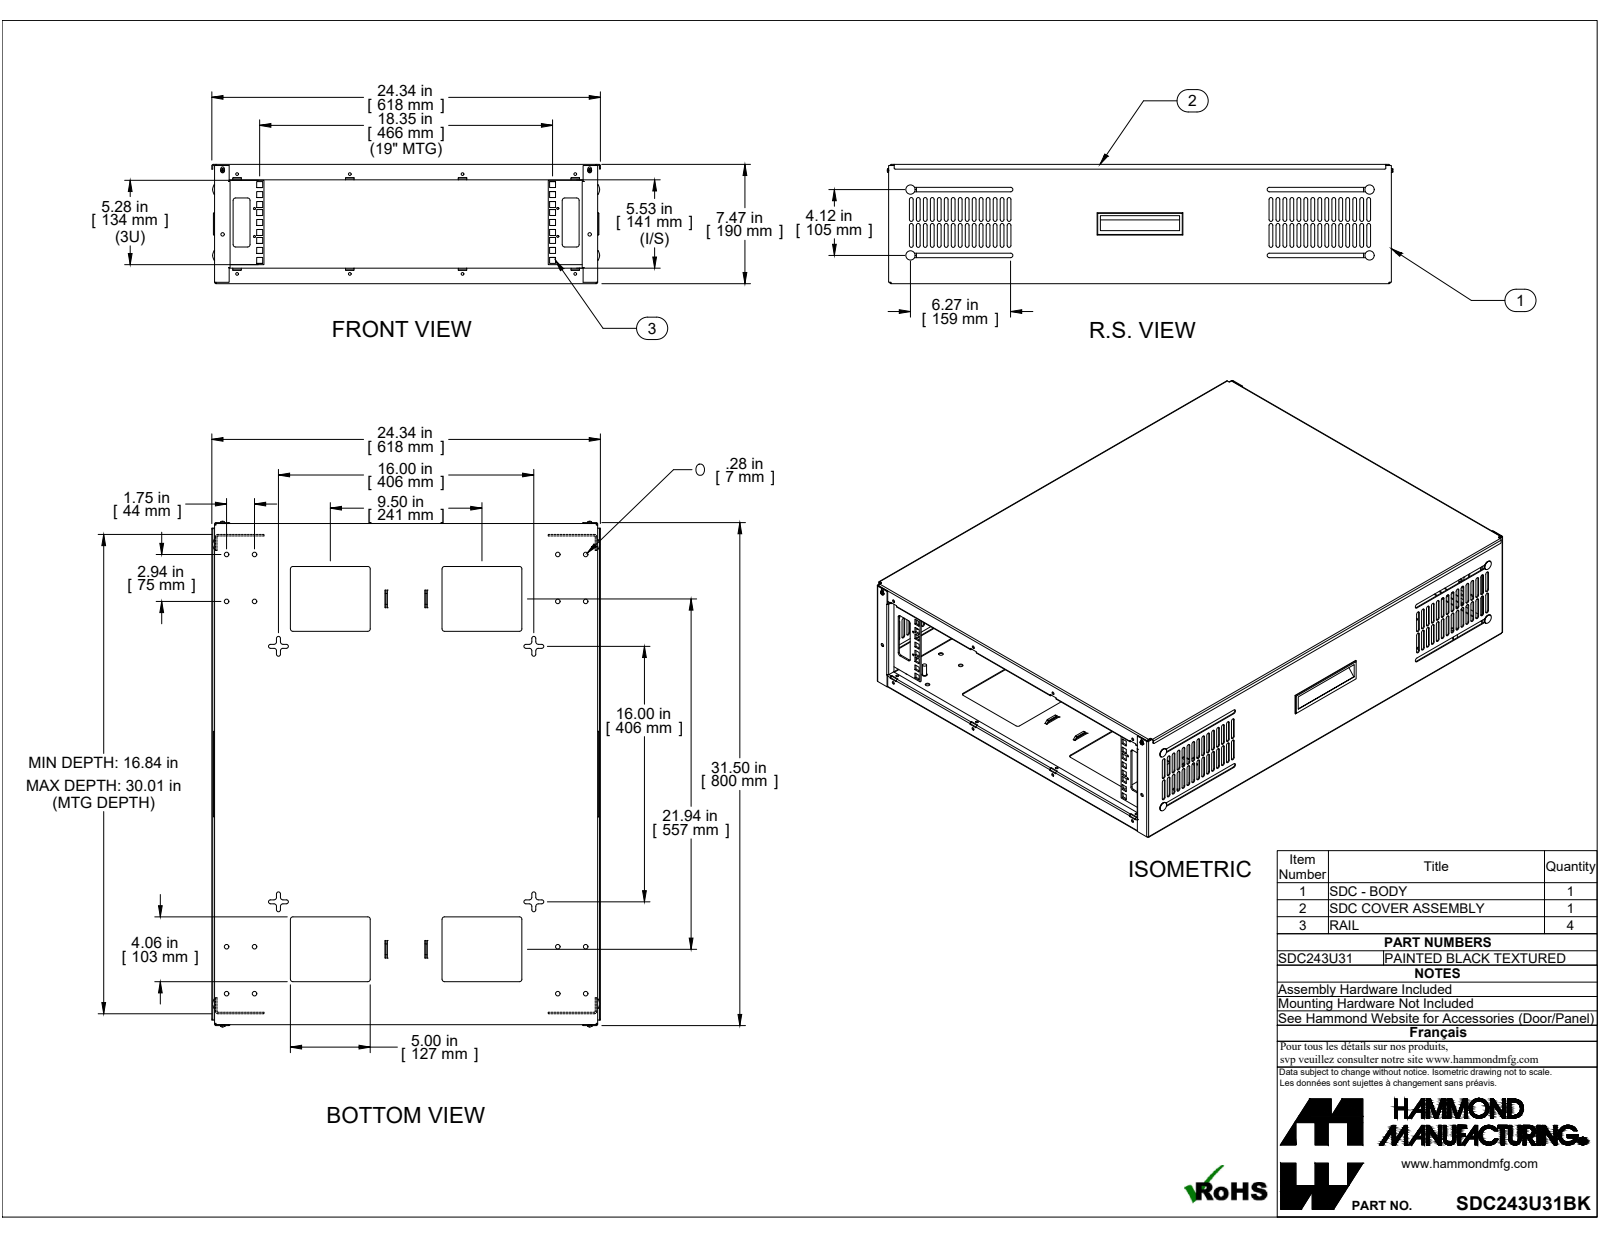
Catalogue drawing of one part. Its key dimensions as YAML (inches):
part_name: "SDC243U31BK"
step_written_by: "SolidWorks 2019 (CONFIG_CONTROL_DESIGN)"
units: inches
bodies: {solids: 37, faces: 1900, planar: 1206, cylindrical: 642, other: 52}
overall_size: [31.67, 24.344, 7.472]
volume: 131
surface_area: 4493
round_holes:
  - {diameter: 0.17, count: 16}
  - {diameter: 0.281, count: 16}
  - {diameter: 0.125, count: 8}
  - {diameter: 0.196, count: 4}
  - {diameter: 0.159, count: 2}
  - {diameter: 0.187, count: 2}
  - {diameter: 0.213, count: 2}
round_bosses_or_shafts:
  - {diameter: 0.25, count: 8}
  - {diameter: 0.58, count: 4}
  - {diameter: 0.313, count: 2}
  - {diameter: 0.28, count: 2}
  - {diameter: 0.187, count: 2}
  - {diameter: 0.138, count: 2}
partial_cylinders:
  - {radius: 0.118, count: 120}
  - {radius: 0.157, count: 44}
  - {radius: 0.029, count: 22}
  - {radius: 0.086, count: 22}
  - {radius: 0.025, count: 16}
  - {radius: 0.125, count: 16}
  - {radius: 0.03, count: 8}
  - {radius: 0.057, count: 8}
face_to_face_distances: [0.057, 7.415, 7.358, 7.472, 23.943, 23.886, 24, 0.072, 7.343, 0.129]
hole_center_spacings: [1.75, 2.937, 3.419, 7.063, 19.005, 19.085, 20.75, 20.957]
